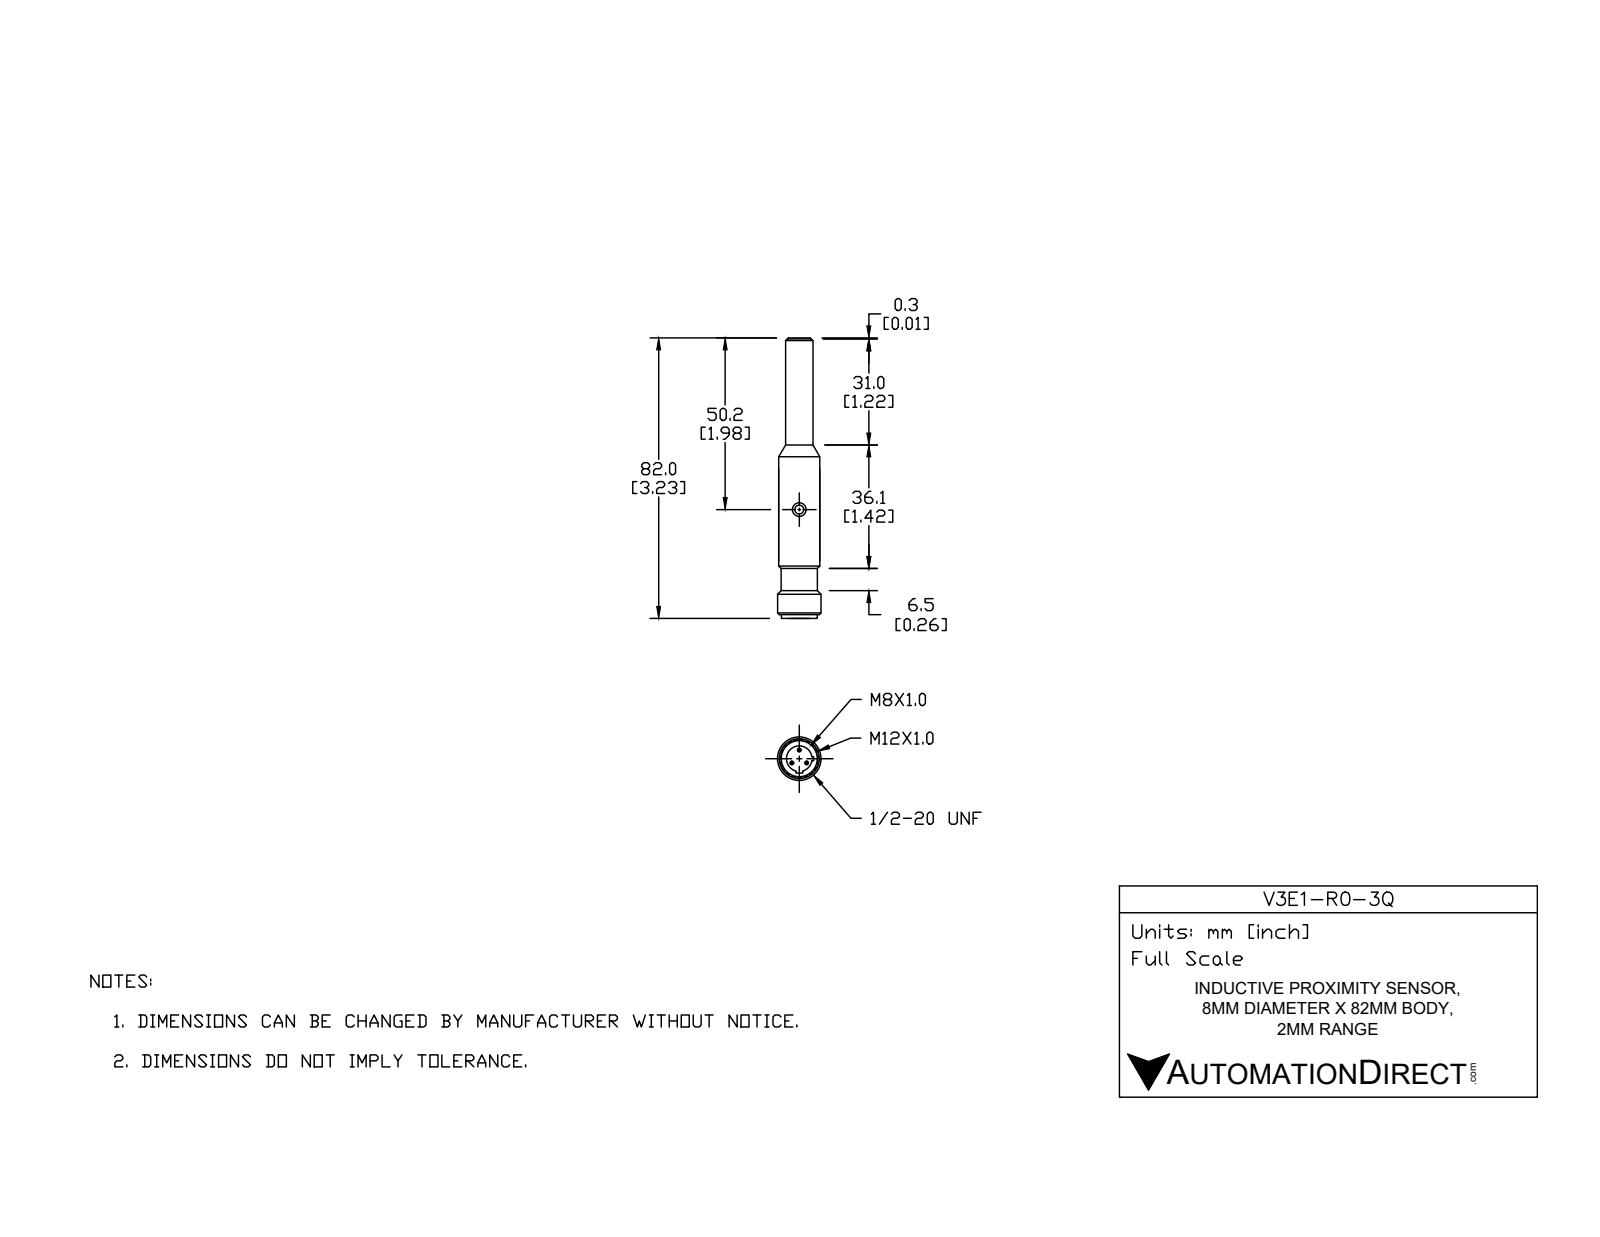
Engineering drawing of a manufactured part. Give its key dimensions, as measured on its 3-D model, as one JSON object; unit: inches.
{"part_name": "V3E1_3Q_fig", "step_written_by": "ST-DEVELOPER v16.7 (AUTOMOTIVE_DESIGN)", "units": "inches", "bodies": {"solids": 3, "faces": 53, "planar": 24, "cylindrical": 19, "other": 10}, "overall_size": [3.224, 0.5, 0.5], "volume_in3": 0.41, "surface_area_in2": 5.259, "round_holes": [[0.039, 3], [0.102, 1], [0.157, 1], [0.295, 1], [0.374, 1]], "round_bosses_or_shafts": [[0.039, 3], [0.5, 1], [0.472, 1], [0.417, 1], [0.413, 1], [0.376, 1], [0.37, 1], [0.315, 1]], "face_to_face_distances": [0.28, 2.945, 3.224, 0.039, 3.185, 0.24, 2.933, 0.374, 0.343, 0.031], "hole_center_spacings": [0.098, 0.17, 0.171]}
